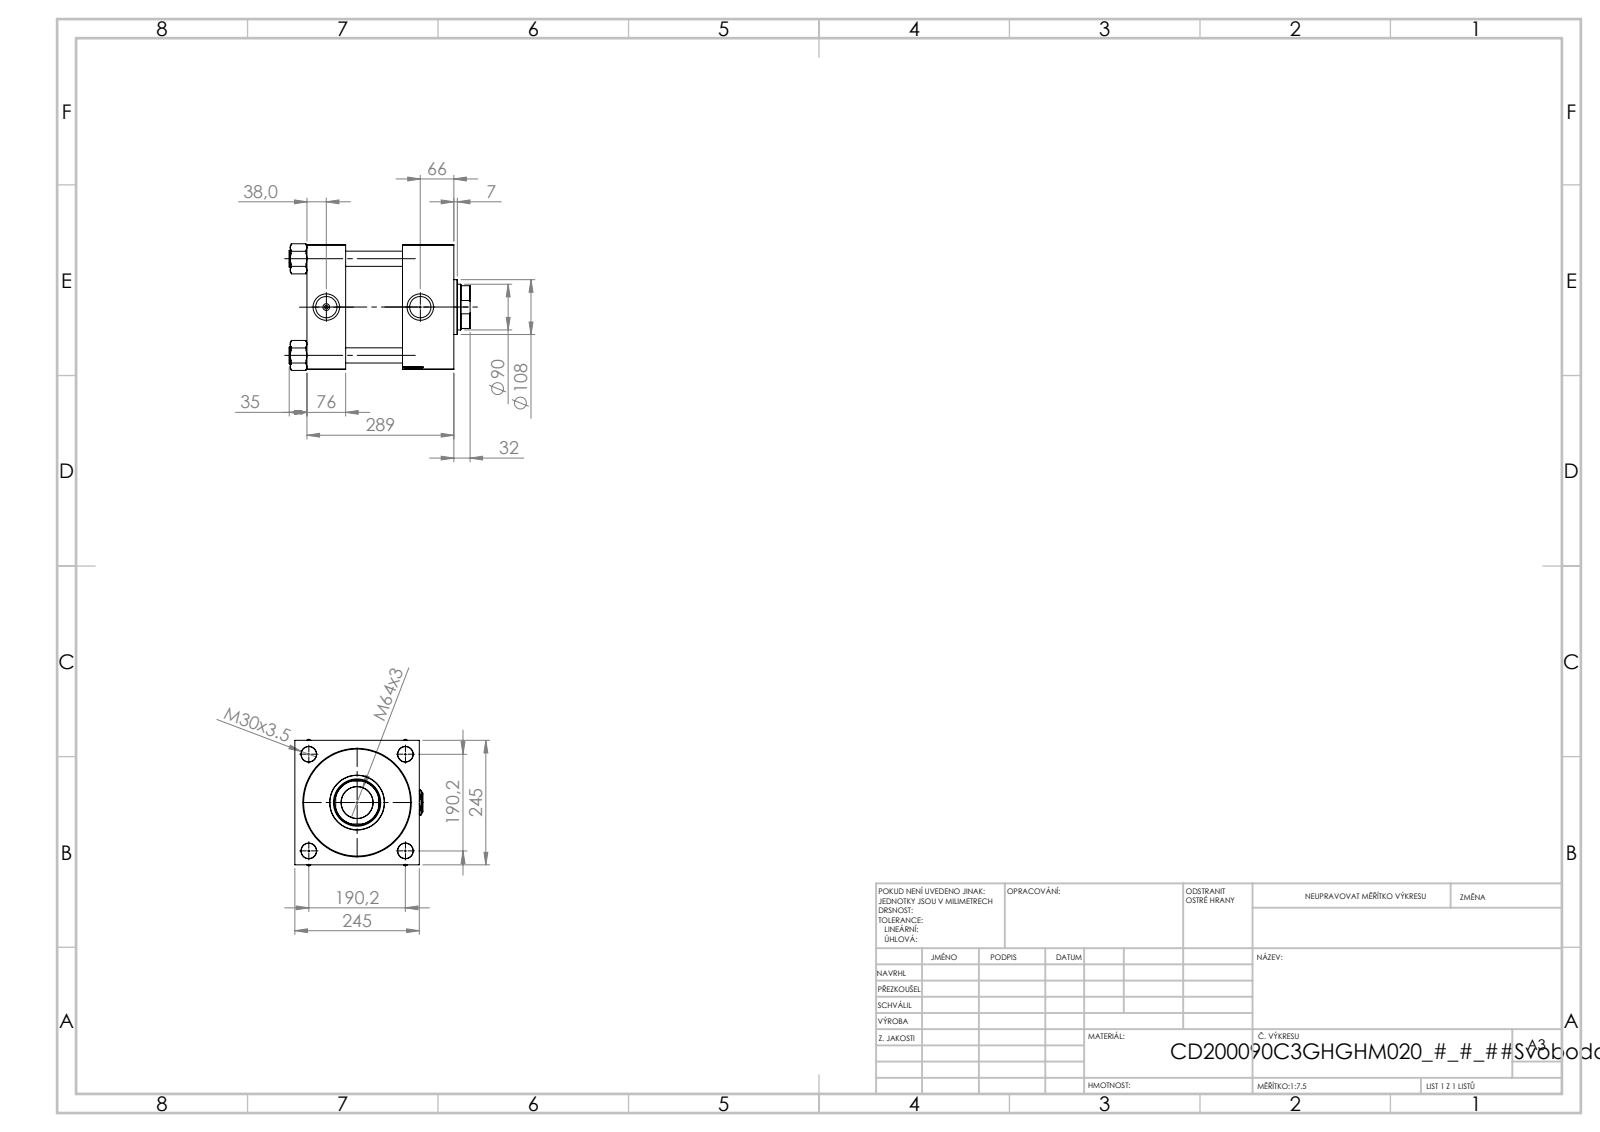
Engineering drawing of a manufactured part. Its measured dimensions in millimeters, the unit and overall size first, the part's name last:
Units: millimetres
Overall size (bounding box): 356 × 252 × 249.44
Round holes (diameter × count): ⌀30 ×4, ⌀7 ×2, ⌀41.92 ×2, ⌀52 ×2, ⌀62.5 ×1, ⌀90 ×1, ⌀93 ×1, ⌀146 ×1, ⌀200 ×1, ⌀210.5 ×1
Round bosses / shafts (diameter × count): ⌀33 ×4, ⌀206 ×1, ⌀108 ×1
Partial cylindrical surfaces — rounded edges, fillets, slot ends (radius × count): R44 ×1
Main face-to-face distances: 245, 76, 289, 213, 260.3, 184.3, 28.7, 188, 112, 72.3
Hole centre spacings: 134.49, 190.2, 268.98, 185
Volume: 13 380 000 mm³ · Surface area: 1 056 000 mm²
Bodies: 13 solids, 1297 faces (621 planar, 98 cylindrical, 578 other)
Part name (STEP PRODUCT): V215CD_VC_C; V215CD_C_TYCINKA; Zatka_pro_OIL_PORT; V215CD_Body_C (+2 more)
STEP written by: SolidWorks 2019 (CONFIG_CONTROL_DESIGN)
